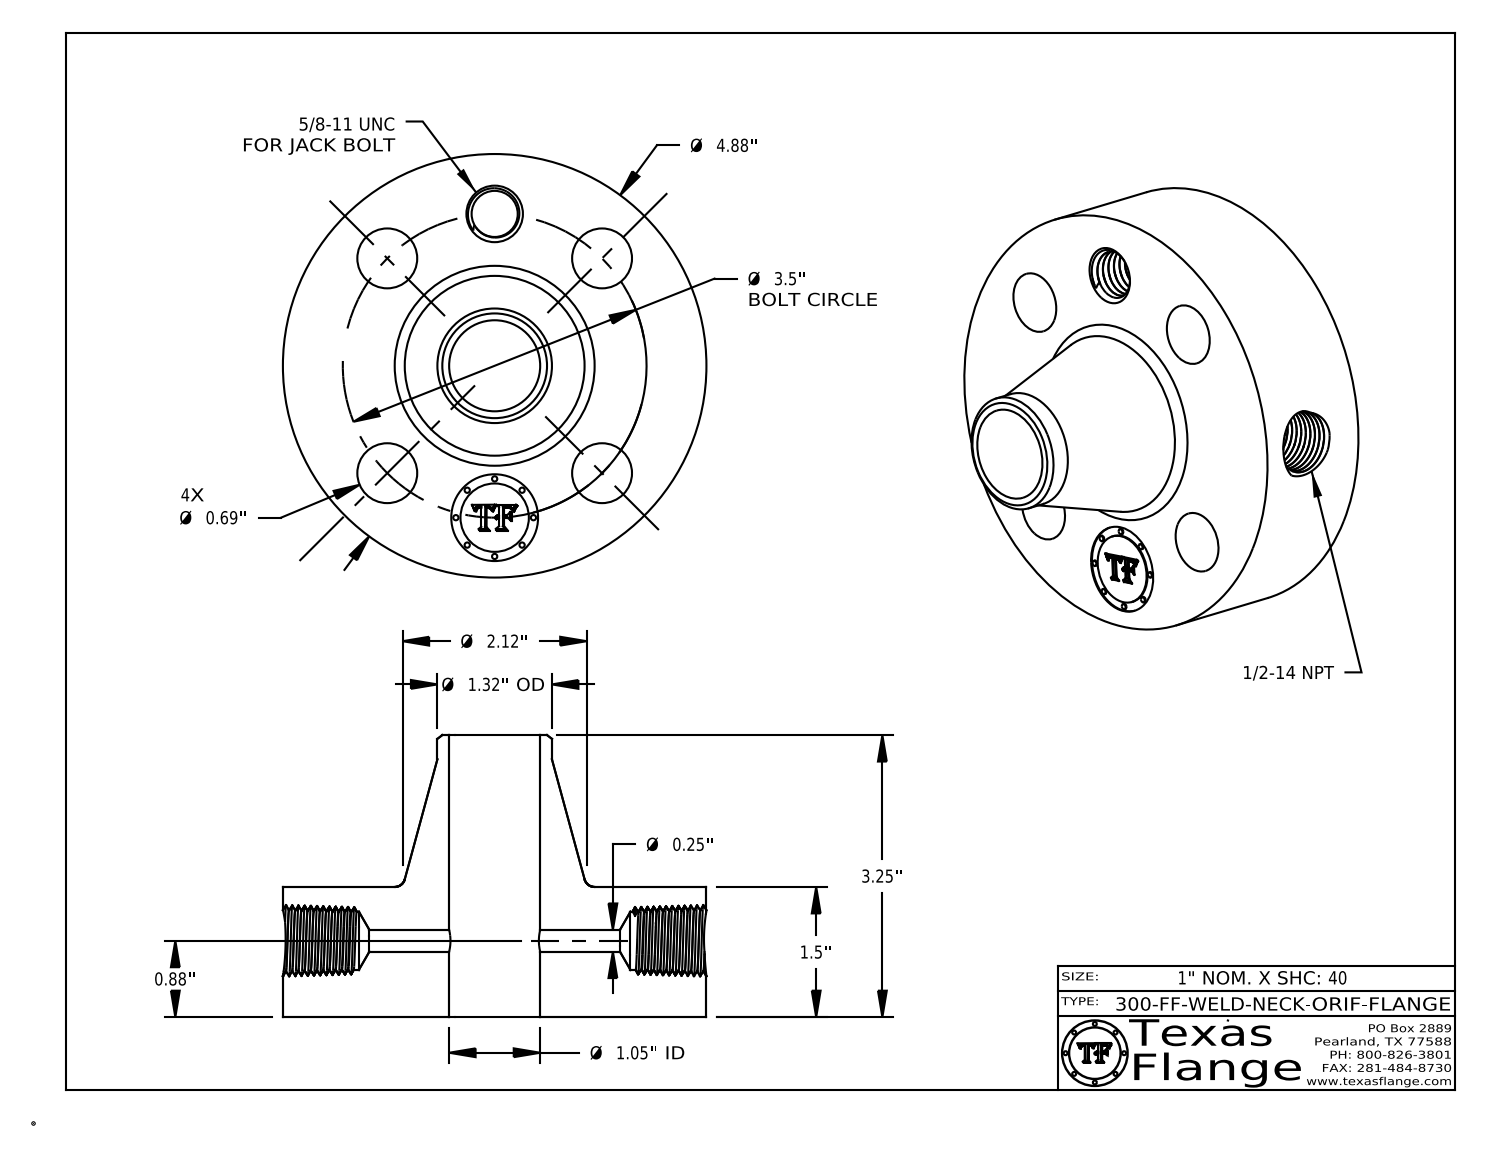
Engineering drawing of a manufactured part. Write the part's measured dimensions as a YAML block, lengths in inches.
part_name: "300-FF-WELD-NECK"
step_written_by: "CATIA V5 STEP AP214 (AUTOMOTIVE_DESIGN)"
units: inches
bodies: {solids: 1, faces: 761, planar: 368, cylindrical: 85, other: 308}
overall_size: [4.88, 4.88, 3.25]
volume: 25.6
surface_area: 98.11
round_holes:
  - {diameter: 0.69, count: 4}
  - {diameter: 0.25, count: 1}
  - {diameter: 0.531, count: 1}
  - {diameter: 0.672, count: 1}
  - {diameter: 1, count: 1}
  - {diameter: 1.049, count: 1}
round_bosses_or_shafts:
  - {diameter: 0.061, count: 8}
  - {diameter: 4.88, count: 1}
  - {diameter: 1.32, count: 1}
  - {diameter: 0.788, count: 1}
face_to_face_distances: [1.5, 1.485, 0.015, 3.25, 1.765, 1.75, 0.298, 0.293, 0.054, 0.248]
hole_center_spacings: [1.75, 1.339, 2.475, 3.233, 3.5]
